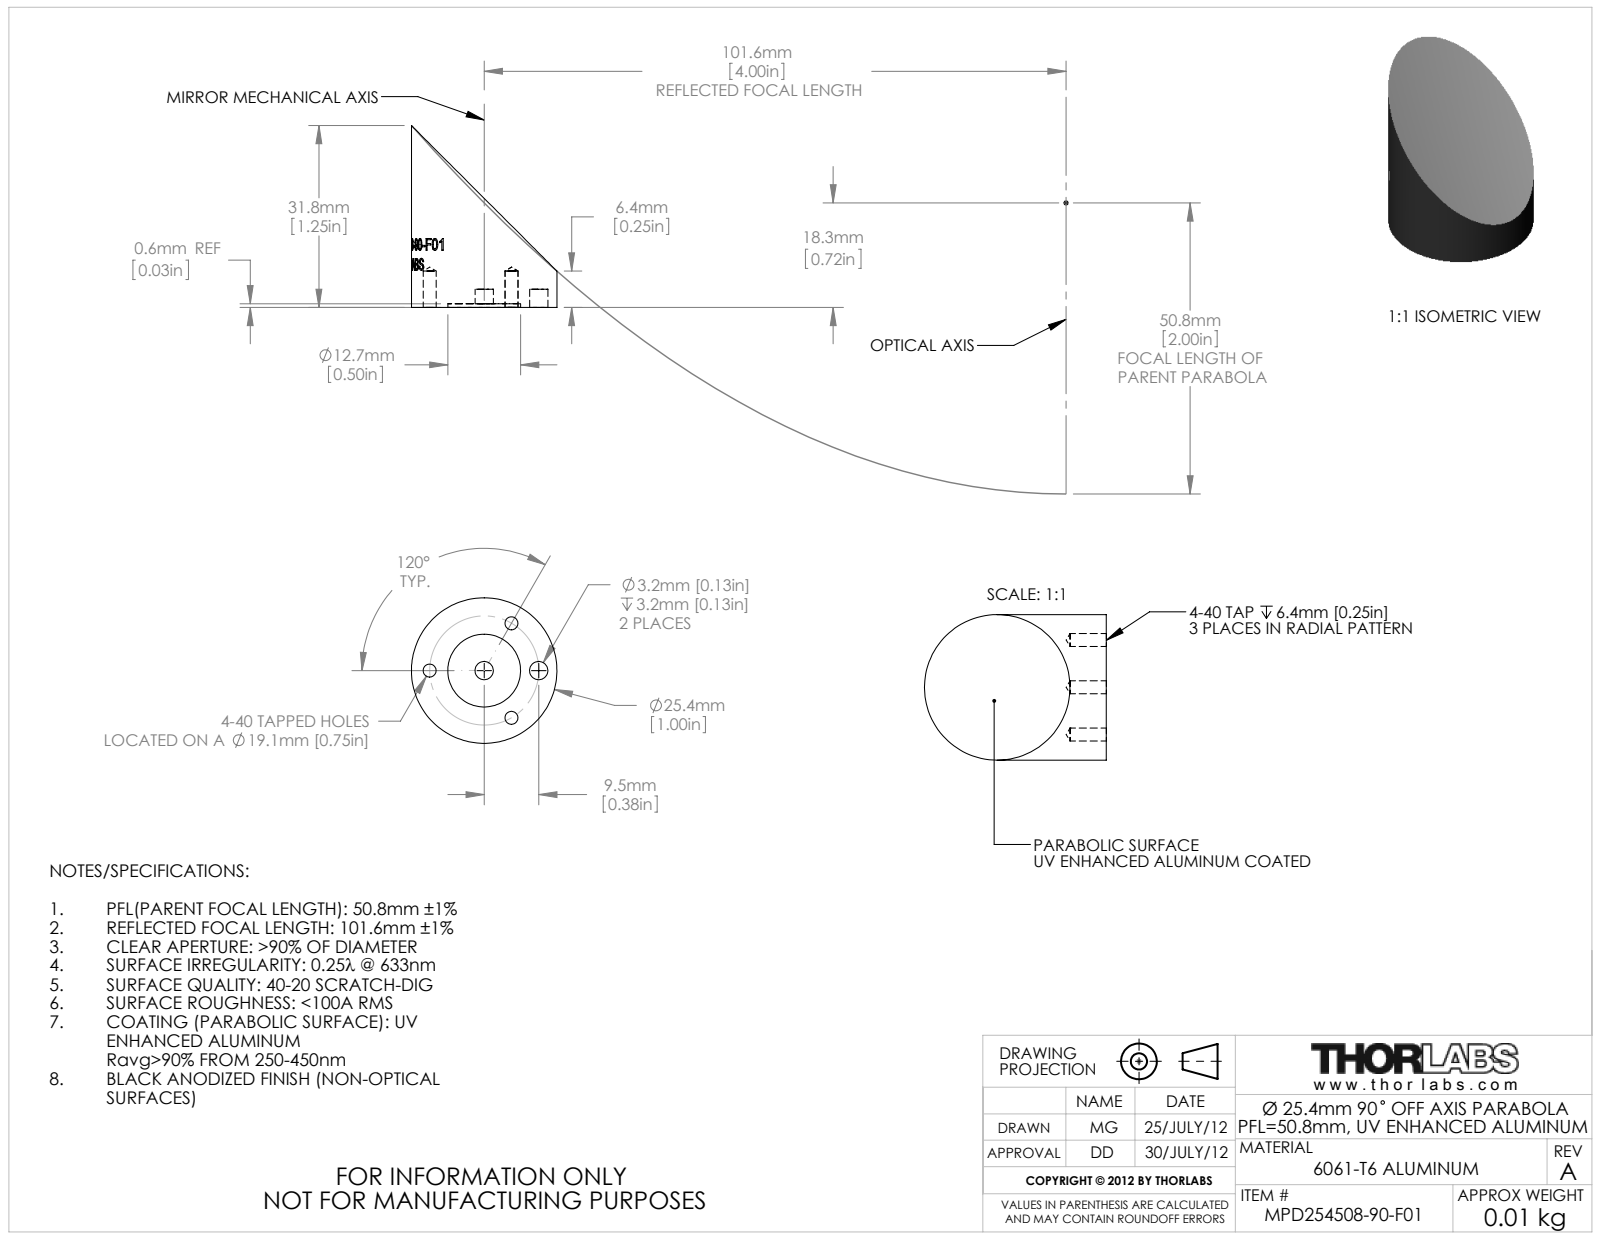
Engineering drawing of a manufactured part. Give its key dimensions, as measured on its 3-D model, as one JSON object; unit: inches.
{"part_name": "24689-E0W", "step_written_by": "SolidWorks 2012 (CONFIG_CONTROL_DESIGN)", "units": "inches", "bodies": {"solids": 1, "faces": 64, "planar": 4, "cylindrical": 52, "other": 8}, "overall_size": [1.25, 1, 1], "volume_in3": 0.564, "surface_area_in2": 4.596, "round_holes": [[0.089, 3], [0.126, 2], [0.5, 1]], "round_bosses_or_shafts": [[1, 1]], "face_to_face_distances": [0.025, 0.125, 0.1], "hole_center_spacings": [0.375, 0.65, 0.375, 0.75]}
